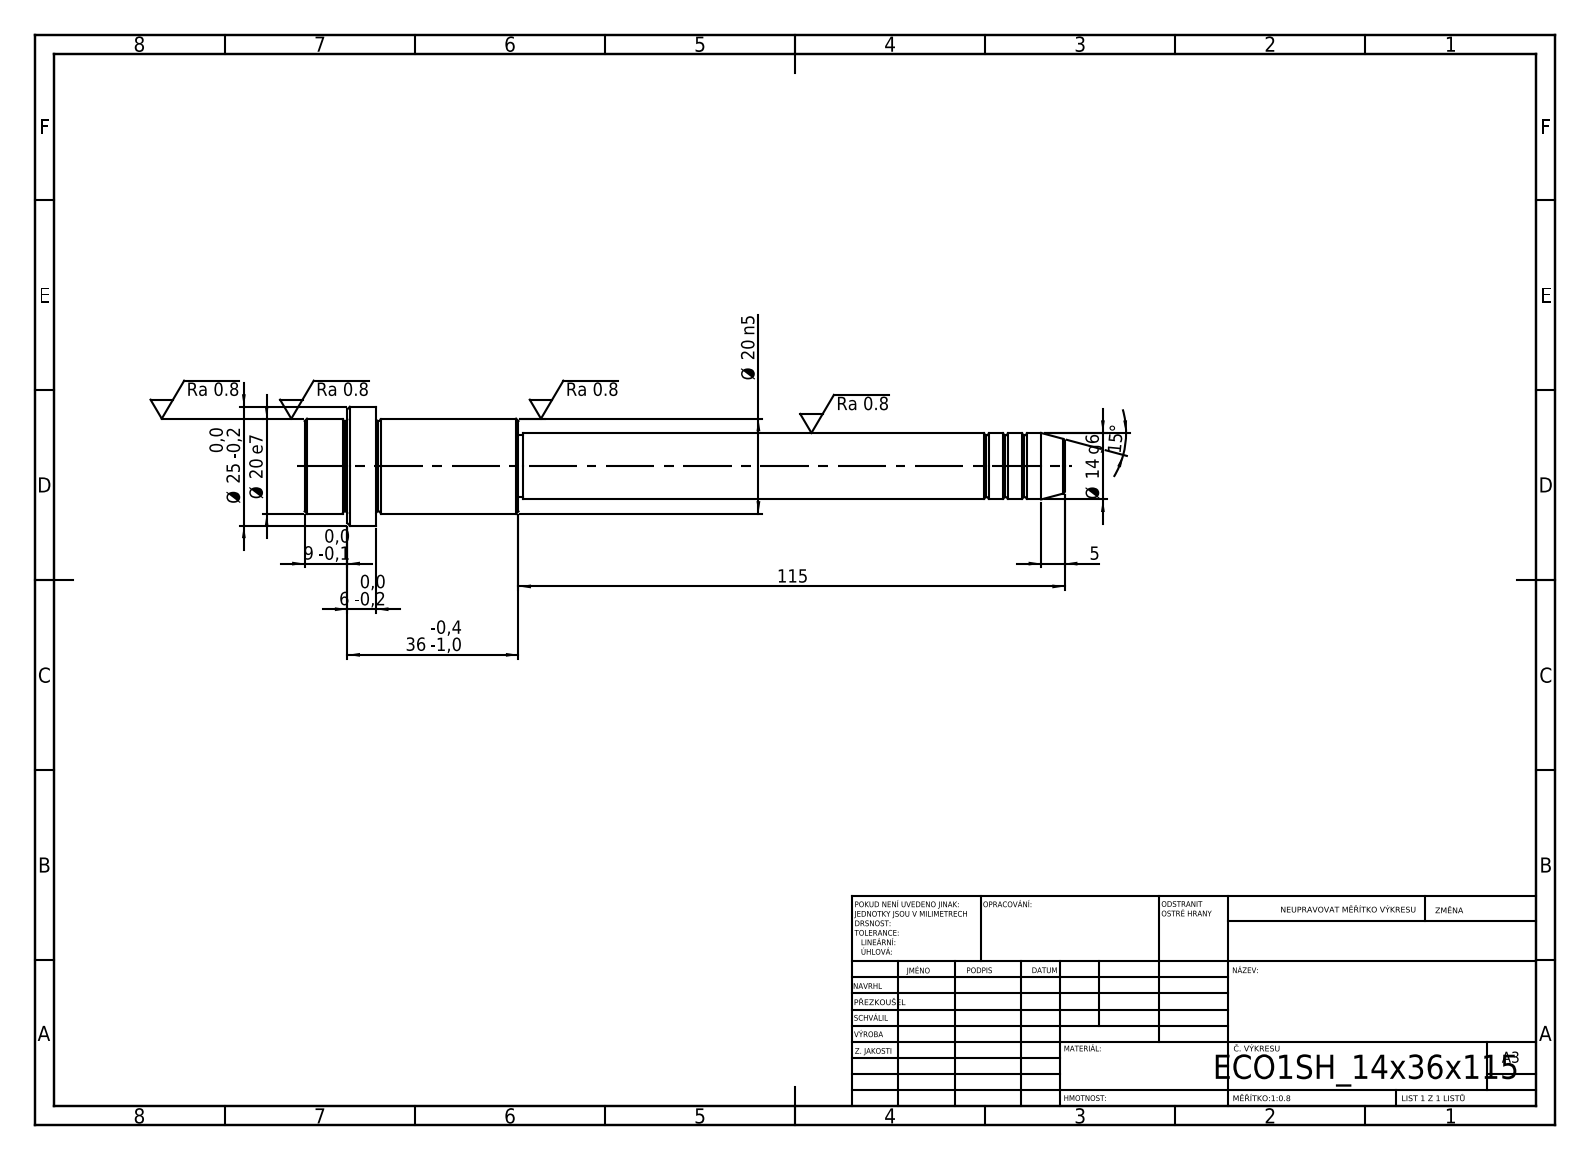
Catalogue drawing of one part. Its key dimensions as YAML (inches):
step_written_by: "SolidWorks 2019 (CONFIG_CONTROL_DESIGN)"
units: inches
bodies: {solids: 1, faces: 52, planar: 6, cylindrical: 16, other: 30}
overall_size: [6.299, 0.984, 0.984]
volume: 1.99
surface_area: 13.95
round_bosses_or_shafts:
  - {diameter: 0.984, count: 1}
  - {diameter: 0.787, count: 1}
  - {diameter: 0.551, count: 1}
  - {diameter: 0.512, count: 1}
face_to_face_distances: [0.591, 1.181, 1.772, 1.417, 0.236, 0.354, 4.528, 5.709, 5.945, 6.299]
